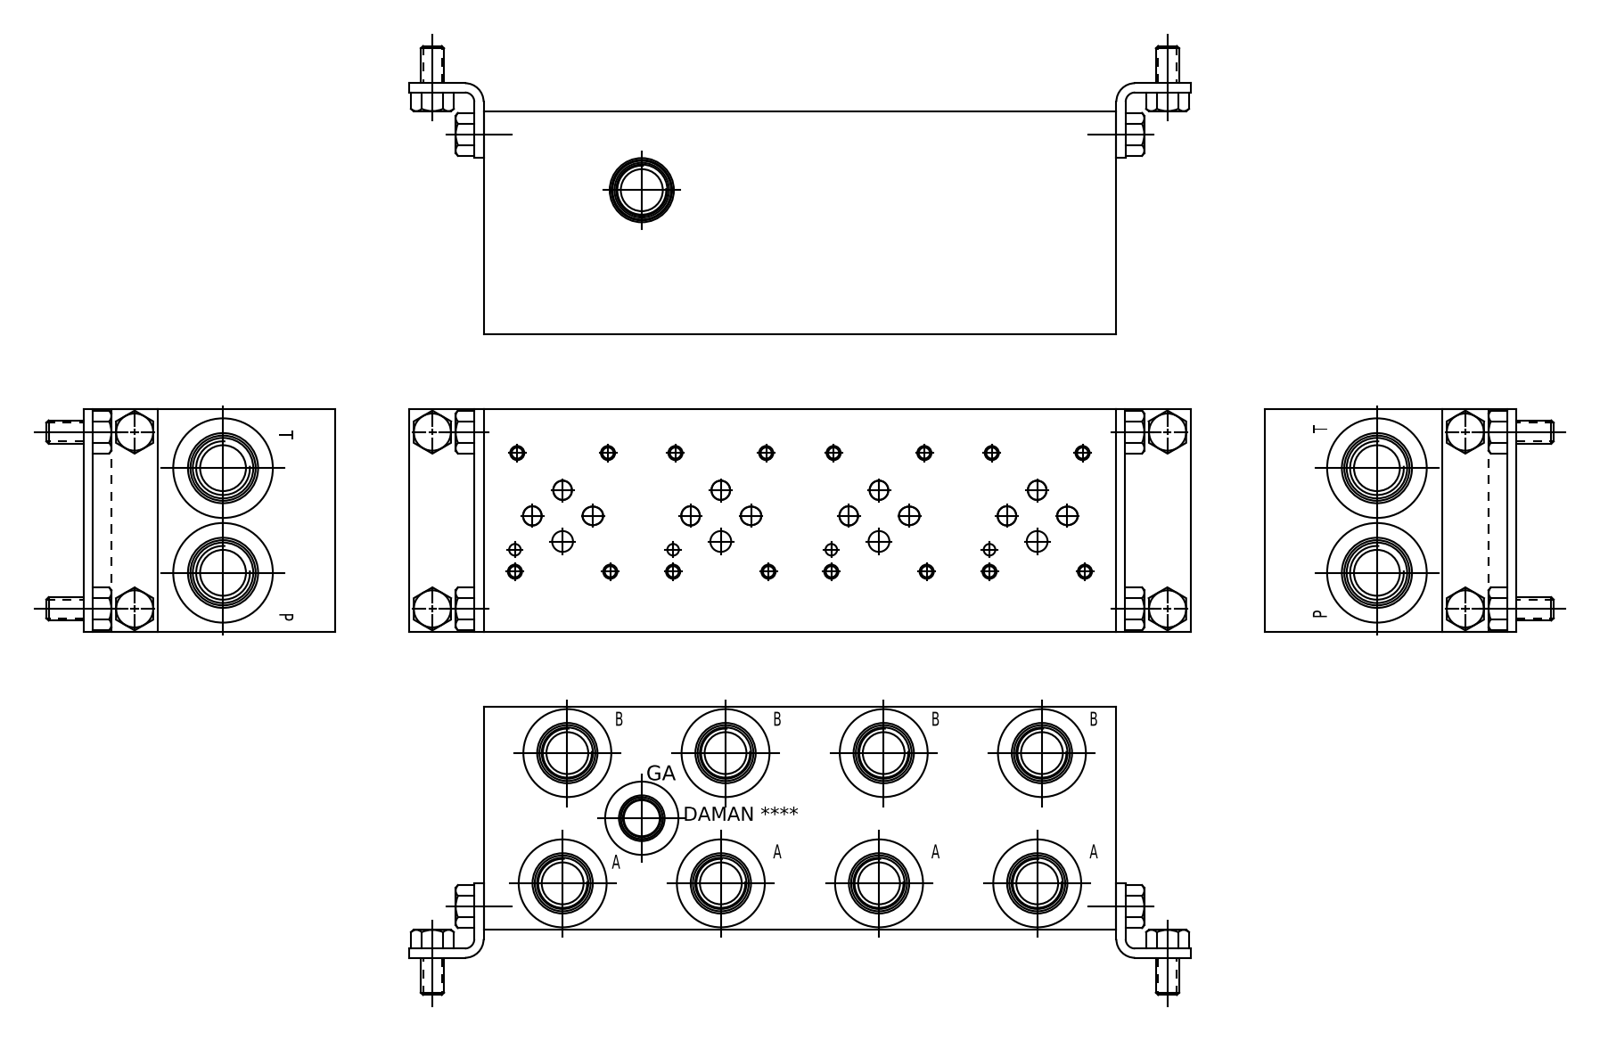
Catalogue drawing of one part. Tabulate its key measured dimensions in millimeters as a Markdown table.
| quantity | value |
| --- | --- |
| part name | Part_AD03S042S~S_3D |
| STEP written by | Autodesk Inventor 2019 (AUTOMOTIVE_DESIGN) |
| units | millimeters |
| bodies | 1 solid, 872 faces (436 planar, 134 cylindrical, 302 other) |
| overall size | 215.9 × 76.2 × 76.2 |
| volume | 1 135 000 mm³ |
| surface area | 106 695 mm² |
| round holes (diameter × count) | 3.78 × 16, 4.83 × 16, 6.35 × 12, 14.3 × 8, 17.5 × 8, 19.05 × 8, 19.25 × 8, 30.63 × 8, 3.96 × 4, 7.14 × 4, 6.53 × 2, 7.92 × 2 |
| main face-to-face distances | 76.2, 0.79, 215.9, 75.41, 215.11, 214.32, 14.27, 61.14, 15.06, 1 |
| hole center spacings | 107.95, 53.98, 53.97, 56.73, 22.05, 33.55, 51.45, 161.93 |
